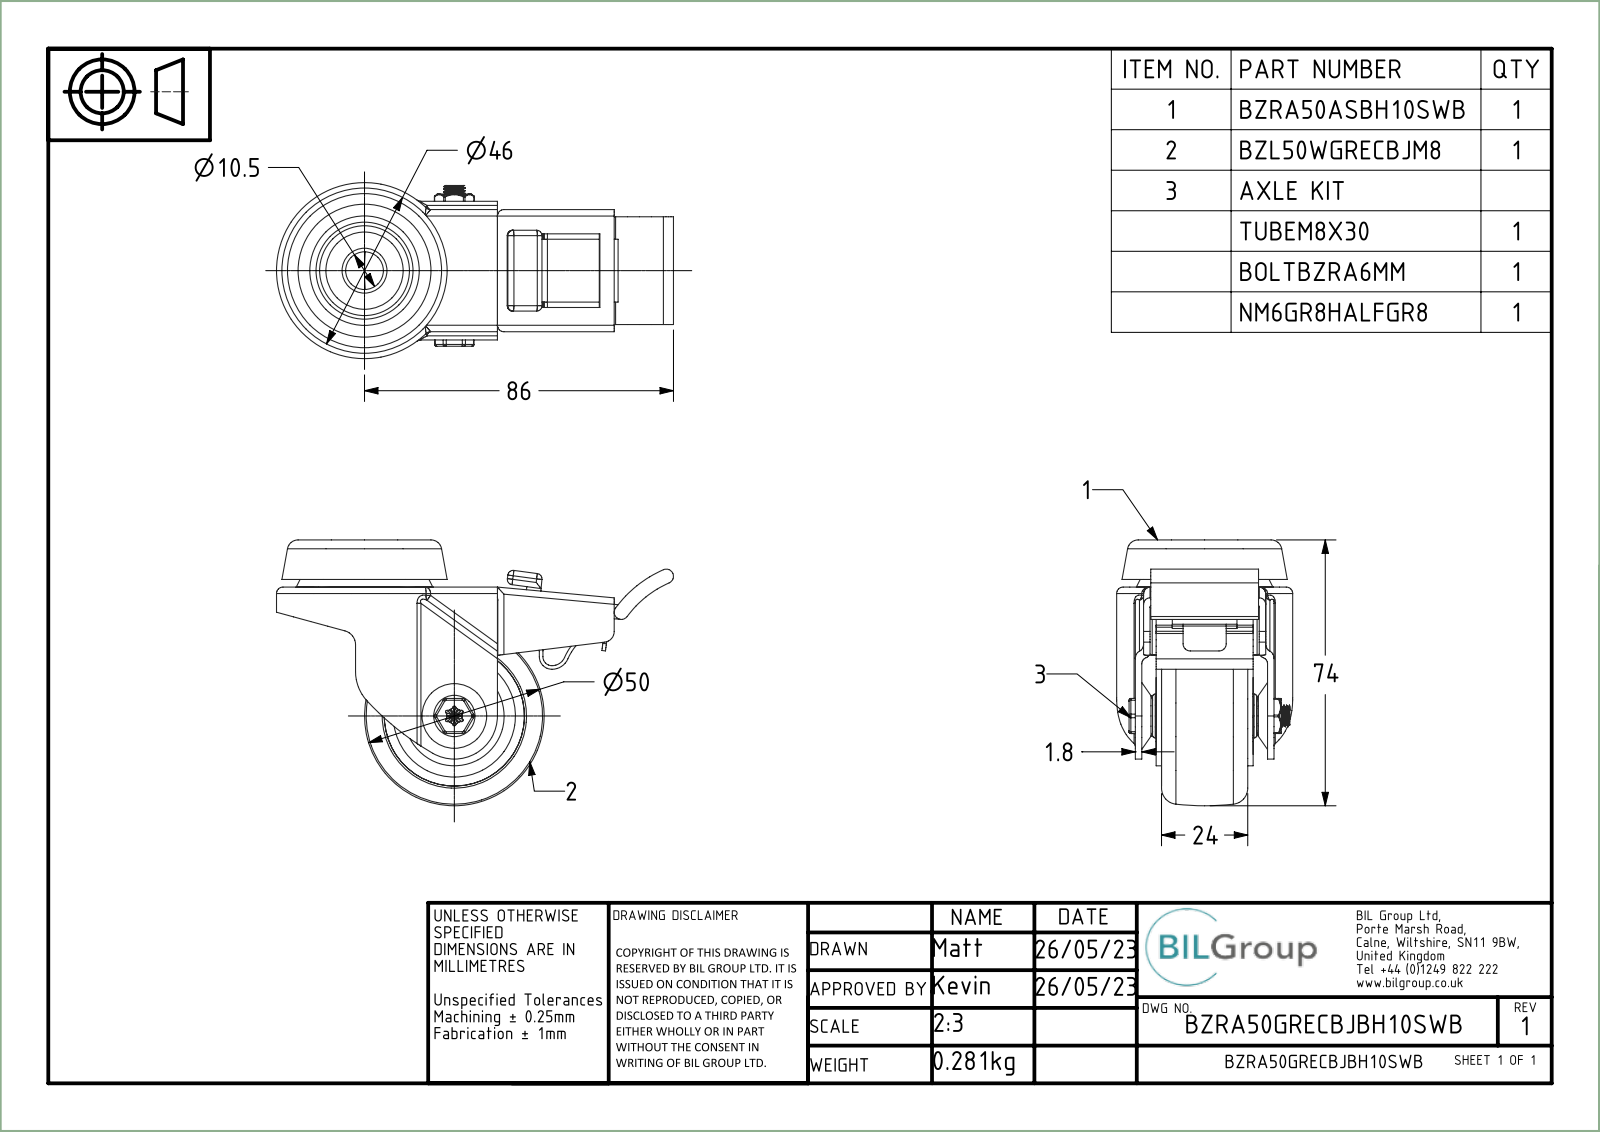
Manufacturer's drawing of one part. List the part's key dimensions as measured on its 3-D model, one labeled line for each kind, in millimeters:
Part name (STEP PRODUCT): BZRA50ASBH10SWB; ZINC PLATED PRESSED STEEL FORKS; ZINC PLATED PRESSED STEEL HEAD; ZINC PLATED PRESSED STEEL BRAKE (+8 more)
STEP written by: Spatial InterOp 3D (CONFIG_CONTROL_DESIGN)
Units: millimetres
Bodies: 32 solids, 727 faces (157 planar, 334 cylindrical, 236 other)
Overall size (bounding box): 110.5 × 74 × 49
Volume: 69 246 mm³ · Surface area: 61 365 mm²
Round holes (diameter × count): ⌀6 ×1, ⌀6.2 ×1, ⌀6.3 ×1, ⌀8.1 ×1, ⌀8.2 ×1, ⌀10.5 ×1, ⌀10.56 ×1, ⌀12.5 ×1, ⌀16 ×1, ⌀19.2 ×1, ⌀20.5 ×1, ⌀22 ×1
Round bosses / shafts (diameter × count): ⌀39 ×1, ⌀38 ×1, ⌀27.75 ×1, ⌀18 ×1, ⌀14.76 ×1, ⌀12.2 ×1, ⌀8 ×1, ⌀7.95 ×1
Partial cylindrical surfaces — rounded edges, fillets, slot ends (radius × count): R1 ×28, R1.8 ×22, R0.5 ×12, R0.9 ×12, R1.5 ×11, R0.4 ×6, R2 ×6, R3 ×3
Main face-to-face distances: 1.8, 1.81, 3.5, 3.2, 1, 10.5, 20, 5, 1.5, 30.4
